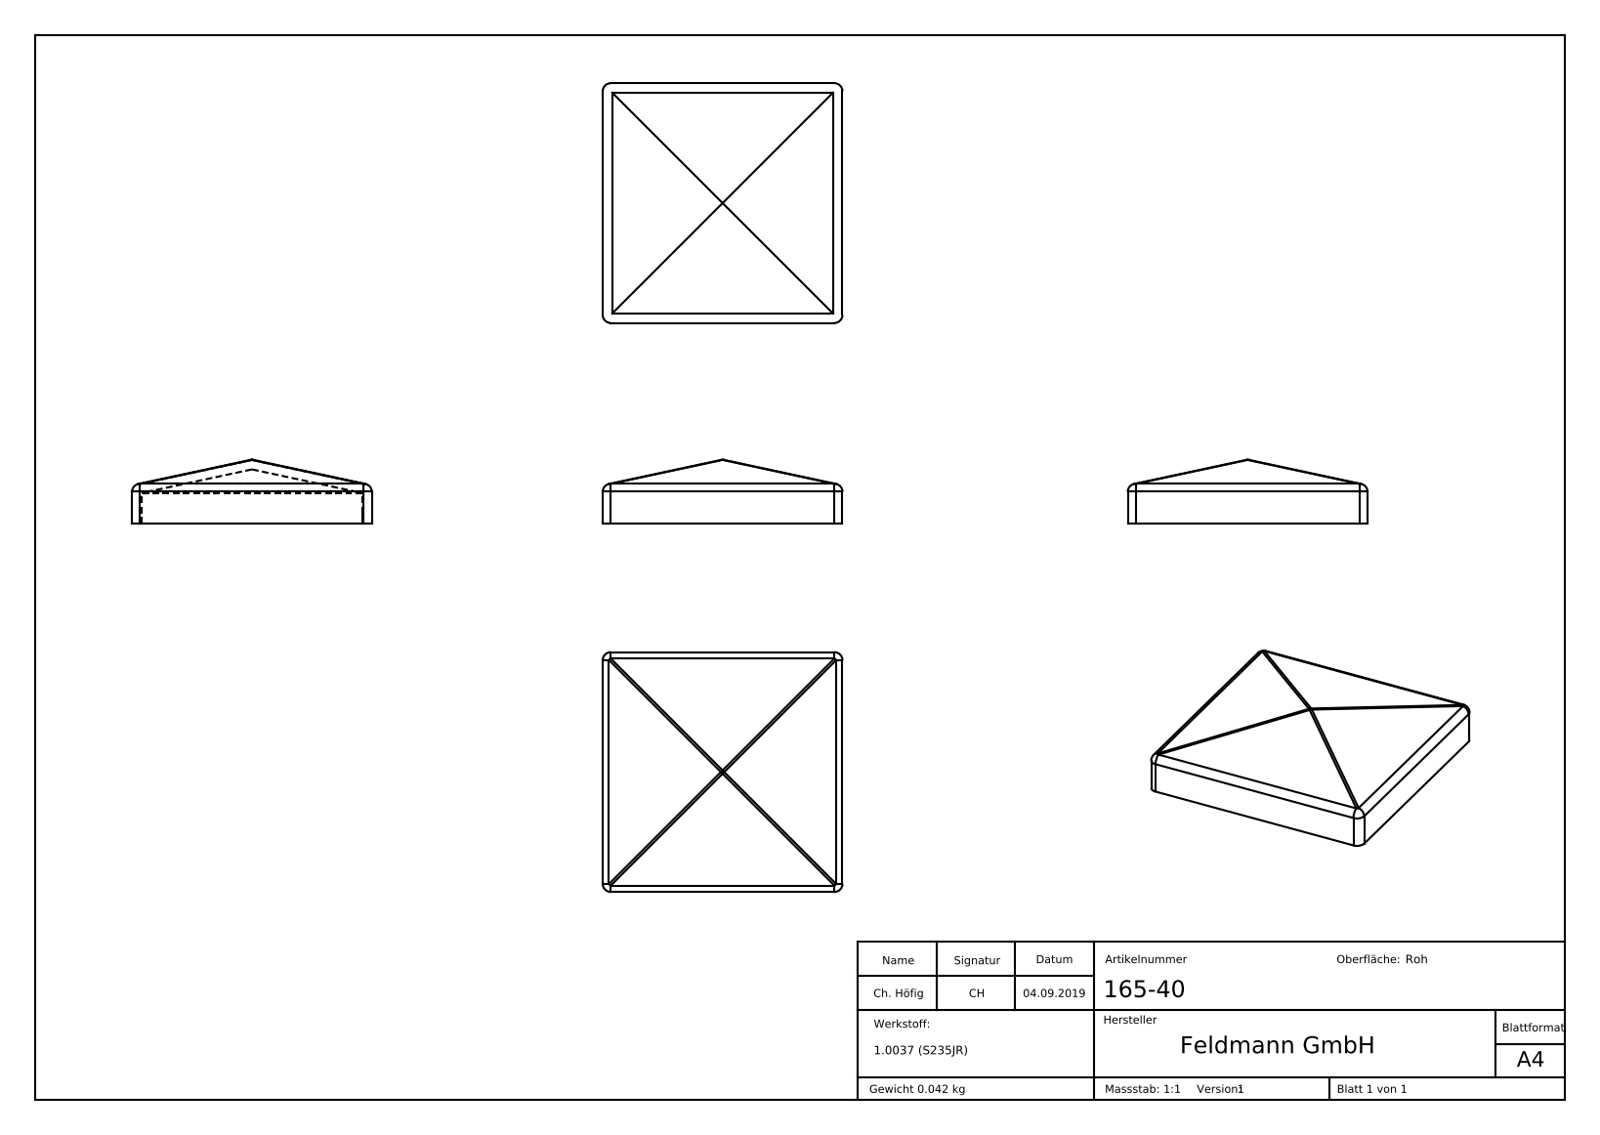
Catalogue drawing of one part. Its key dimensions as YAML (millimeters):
part_name: "165-40"
step_written_by: "SolidWorks 2015 (CONFIG_CONTROL_DESIGN)"
units: millimeters
bodies: {solids: 1, faces: 322, planar: 170, cylindrical: 12, other: 140}
overall_size: [45, 45, 12]
volume: 5392
surface_area: 6306
partial_cylinders:
  - {radius: 1.5, count: 12}
face_to_face_distances: [1.8, 43.2, 45, 41.4, 1.7, 41.5, 43.3, 6.36, 1, 0.58]
